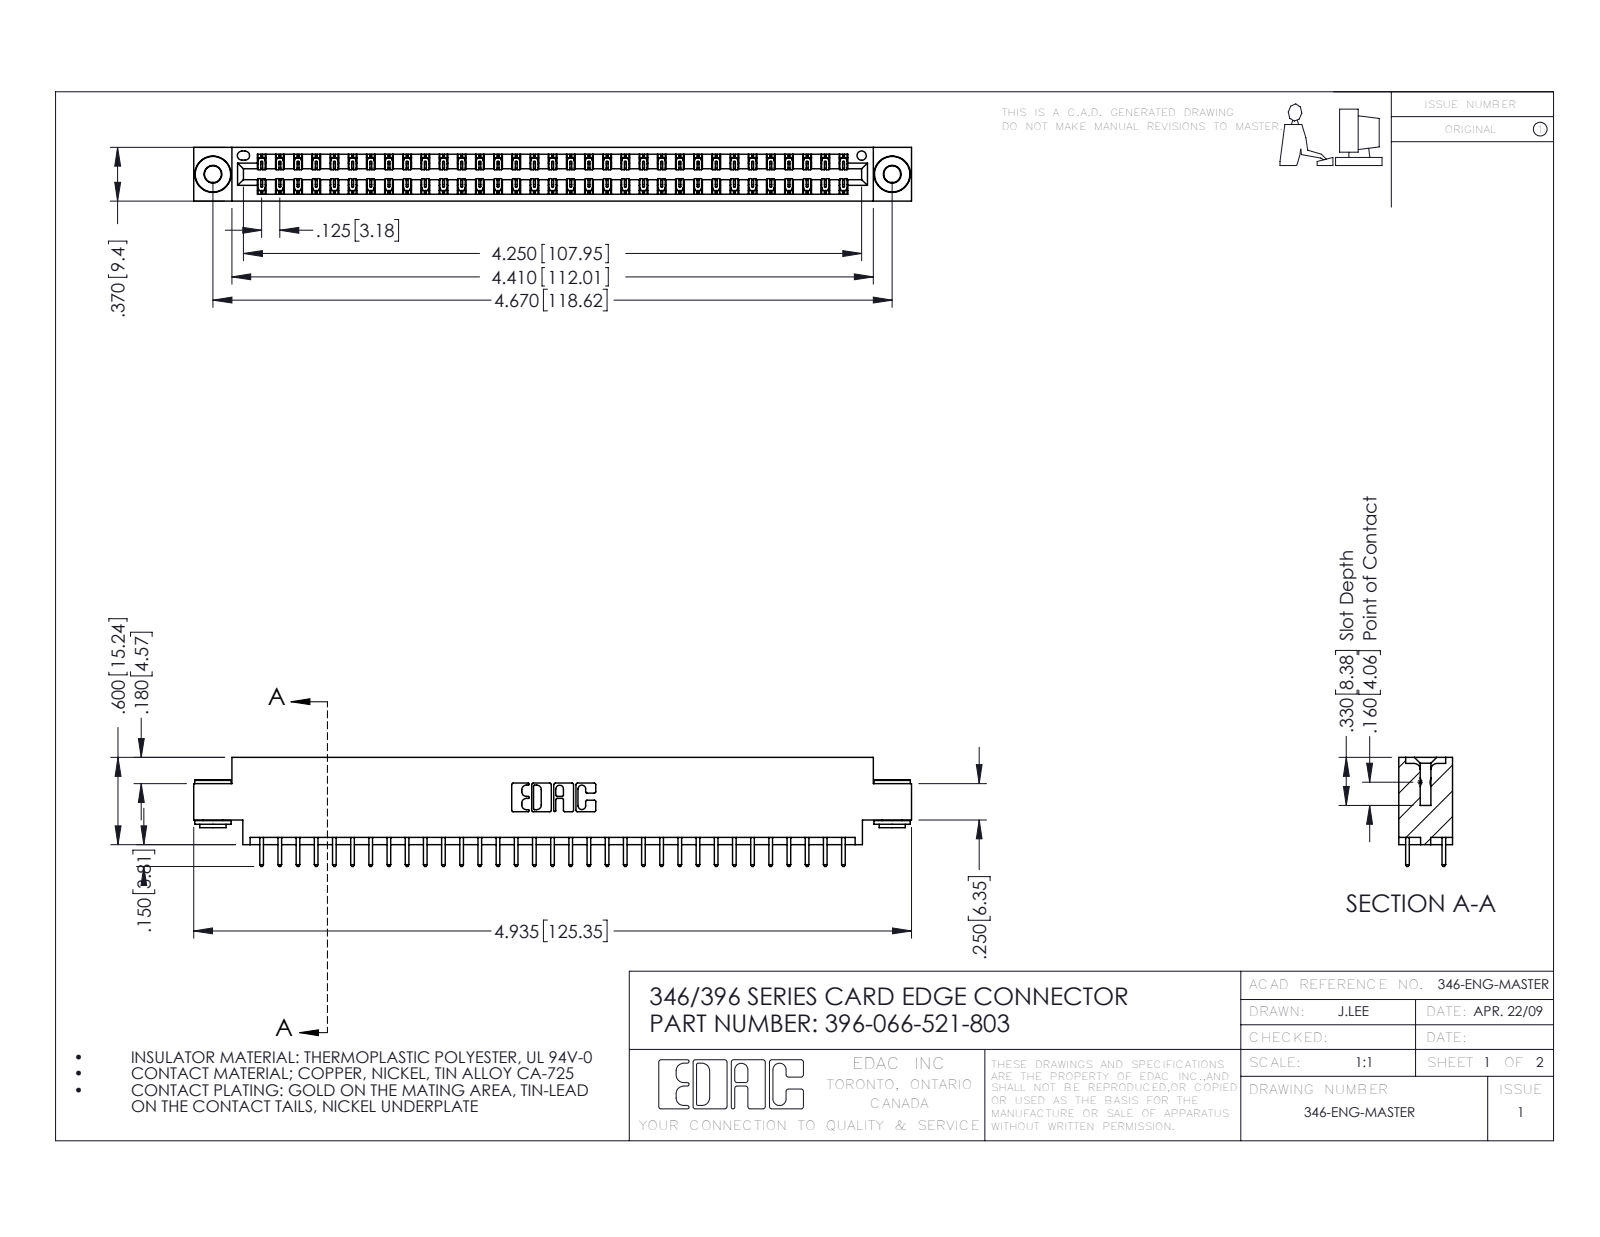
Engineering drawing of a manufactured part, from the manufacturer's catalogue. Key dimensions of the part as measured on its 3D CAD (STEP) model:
Part name (STEP PRODUCT): 345-250-002_345-250-002-102; 345-292-001_345-293-121; 396-066-521-803; 346 Part_0.170 Offset - 0.156 Dia-TH
STEP written by: SolidWorks 2016 (CONFIG_CONTROL_DESIGN)
Units: inches
Bodies: 69 solids, 3596 faces (2400 planar, 1188 cylindrical, 8 other)
Overall size (bounding box): 4.935 × 0.75 × 0.37
Volume: 0.732 in³ · Surface area: 25.66 in²
Round holes (diameter × count): ⌀0.116 ×2, ⌀0.156 ×2, ⌀0.064 ×1
Round bosses / shafts (diameter × count): ⌀0.25 ×2, ⌀0.18 ×2, ⌀0.136 ×2
Partial cylindrical surfaces — rounded edges, fillets, slot ends (radius × count): R0.006 ×99, R0.01 ×66, R0.01 ×22, R0.007 ×6, R0.031 ×6, R0.026 ×3, R0.014 ×2, R0.022 ×2
Main face-to-face distances: 0.048, 0.322, 0.37, 0.25, 0.025, 0.072, 0.298, 0.275, 0.148, 0.222
Hole centre spacings: 0.246, 4.462, 4.67
